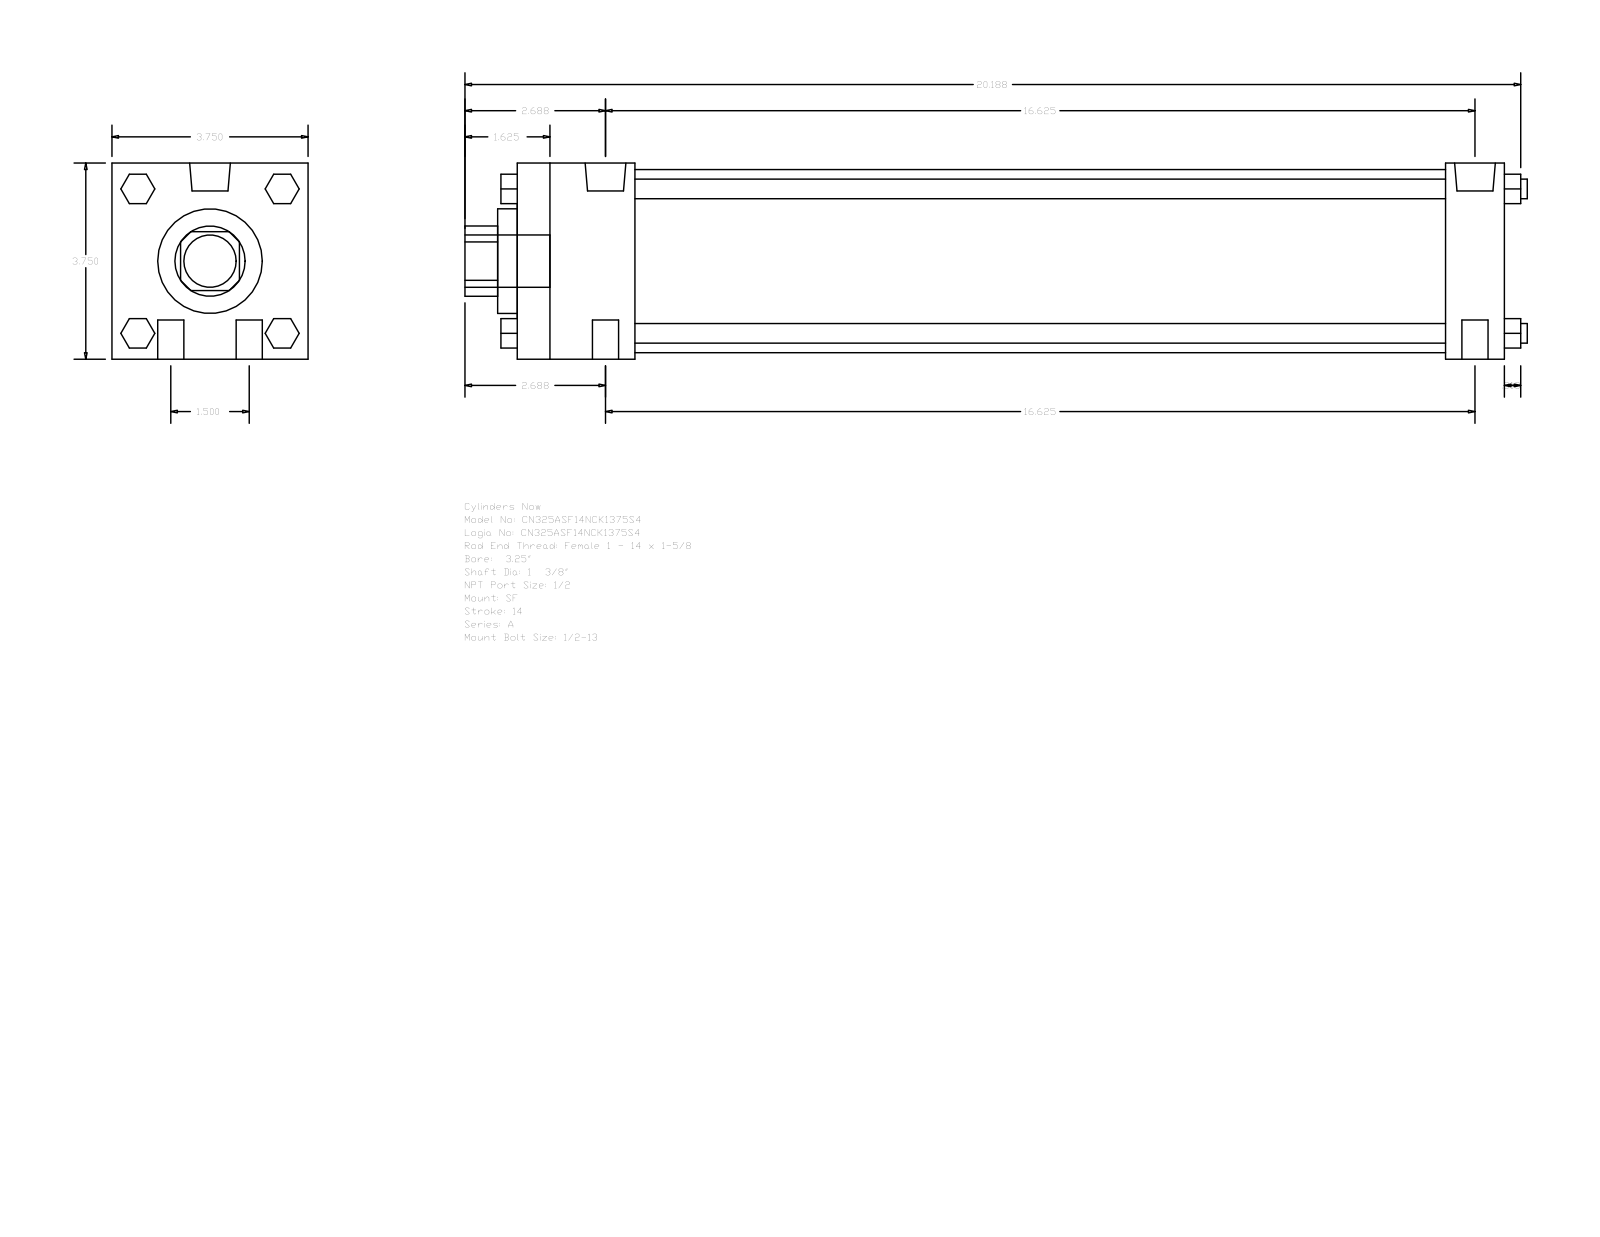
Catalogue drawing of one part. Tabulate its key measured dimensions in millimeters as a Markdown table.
| quantity | value |
| --- | --- |
| part name | A_SF__0325_1.375 |
| STEP written by | GSSL Pune (CONFIG_CONTROL_DESIGN) |
| units | millimeters |
| bodies | 0 solids, 124 faces (94 planar, 30 cylindrical, 0 other) |
| overall size | 515.94 × 95.25 × 95.25 |
| round holes (diameter × count) | 34.92 × 1, 50.8 × 1, 88.9 × 1 |
| round bosses / shafts (diameter × count) | 12.7 × 4, 9.53 × 4, 19.77 × 2, 8.73 × 2, 25.4 × 1 |
| partial cylindrical surfaces (radius × count) | 17.06 × 1 |
| main face-to-face distances | 95.24, 479.42, 28.57, 450.85, 57.15, 393.7, 422.27, 9.52, 66.67, 460.37 |
